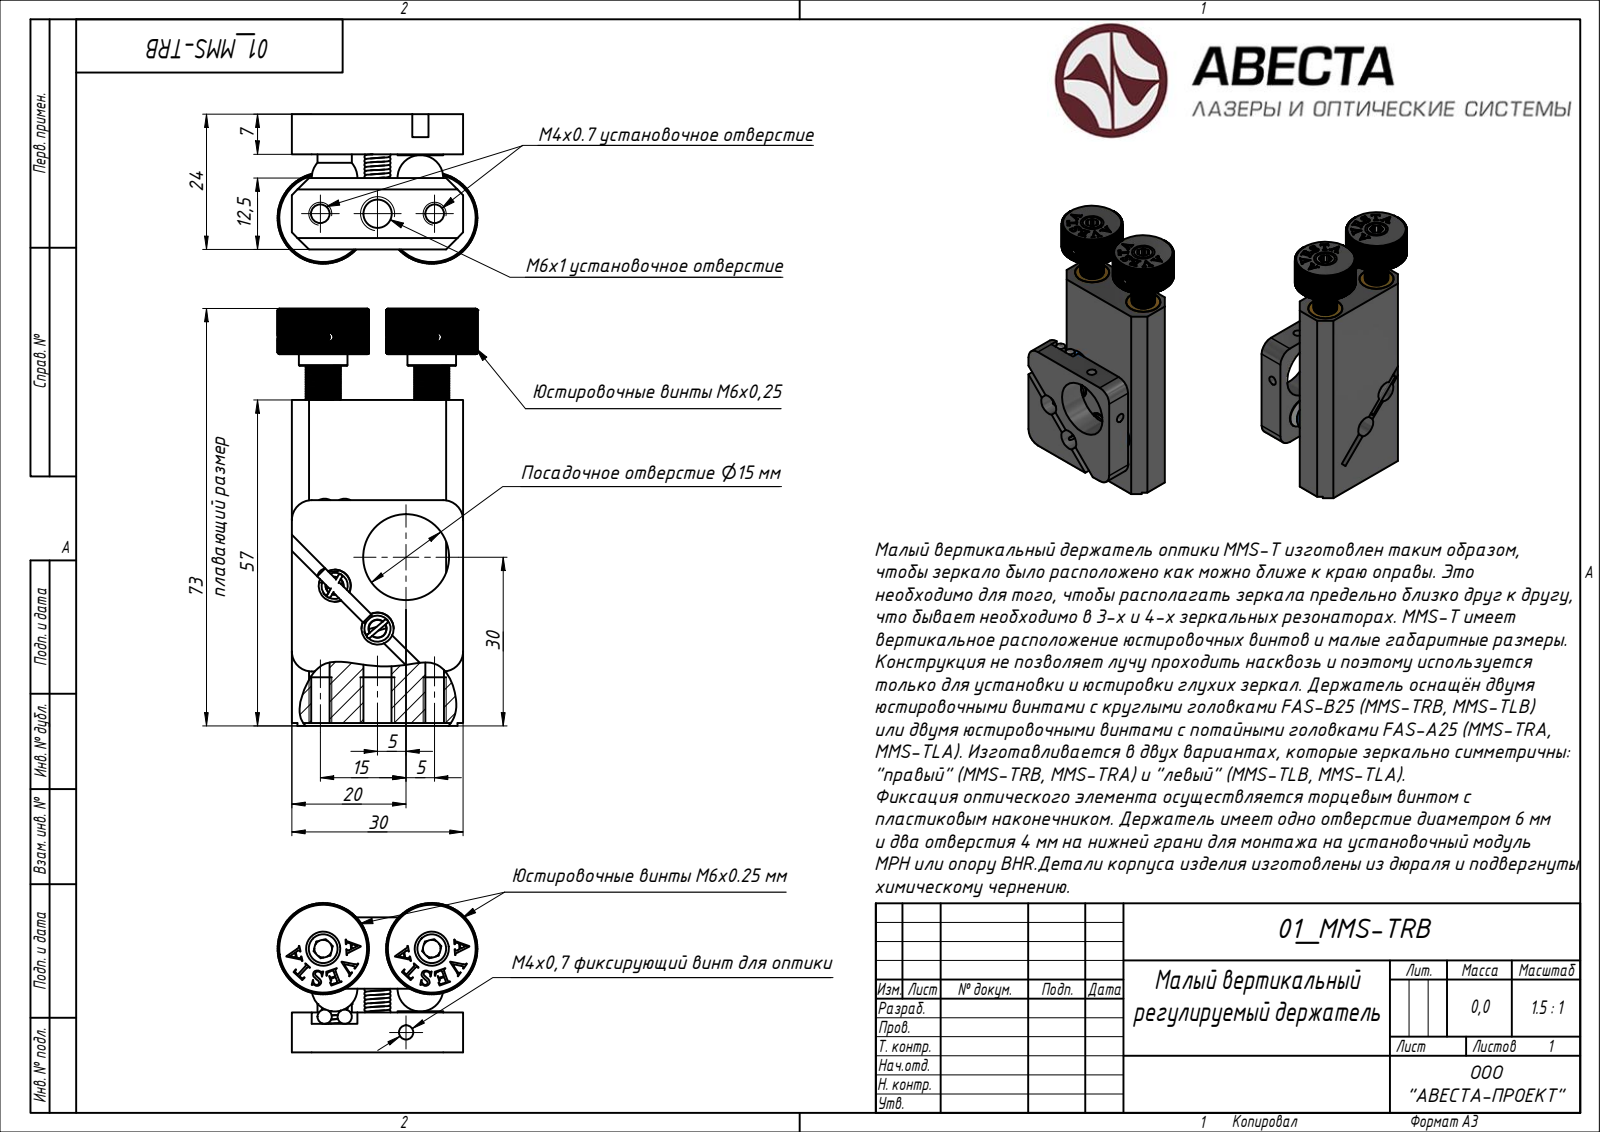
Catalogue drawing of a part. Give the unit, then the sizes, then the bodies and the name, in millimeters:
Units: millimetres
Overall size (bounding box): 75.64 × 35 × 26.16
Main face-to-face distances: 12.5, 30, 11.16, 23.66, 16.66, 2, 7, 25.81, 4.16, 10.64
Volume: 25 997 mm³ · Surface area: 17 700 mm²
Bodies: 17 solids, 612 faces (292 planar, 0 cylindrical, 320 other)
STEP written by: ST-DEVELOPER v15 (AUTOMOTIVE_DESIGN)
